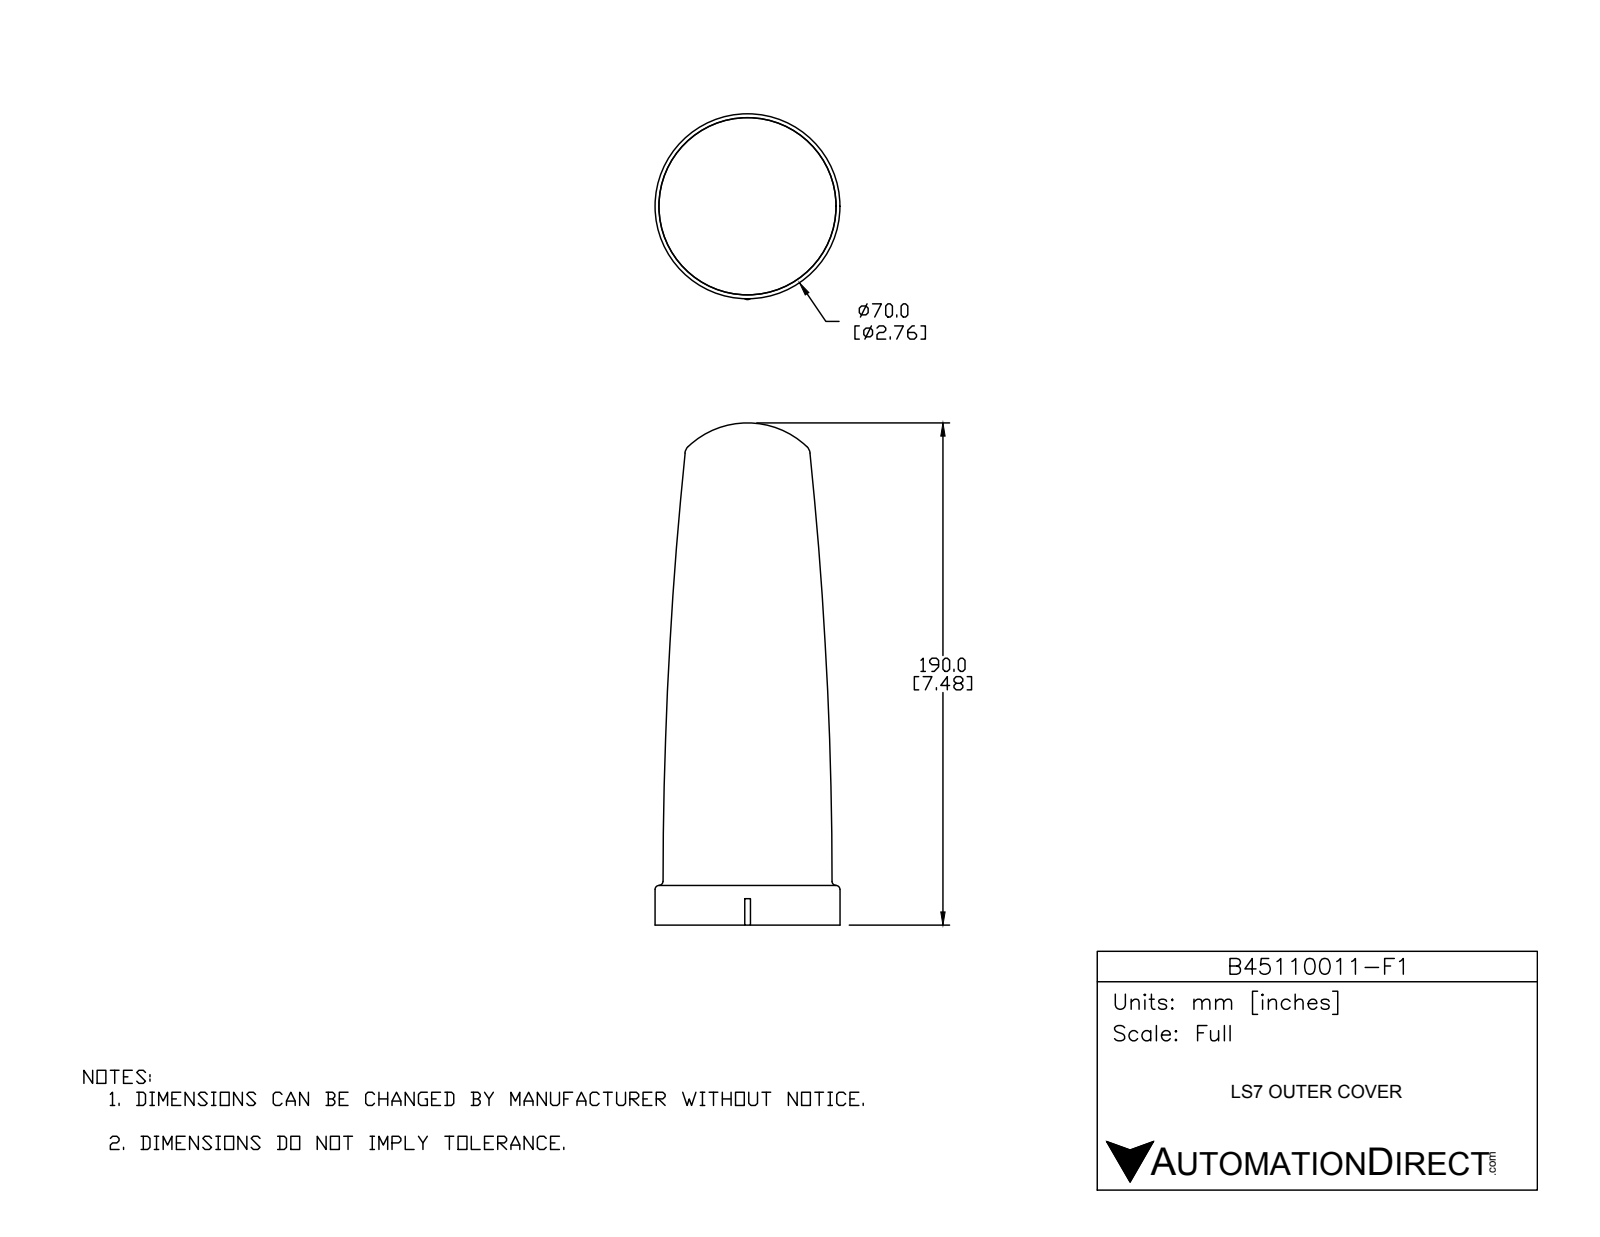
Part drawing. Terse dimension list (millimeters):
name: B45110011-F1
written by: SolidWorks 2016 (AUTOMOTIVE_DESIGN)
unit: mm
bodies: 1 solid, 26 faces (4 planar, 6 cylindrical, 16 other)
size: 190 × 70.3 × 70
volume: 59 155 mm³; area: 69 976 mm²
holes: 1× ⌀66.6
bosses: 1× ⌀70
rounds: 1× R1, 1× R2
face distances: 9.4, 10, 0.6, 15, 5.6, 5
